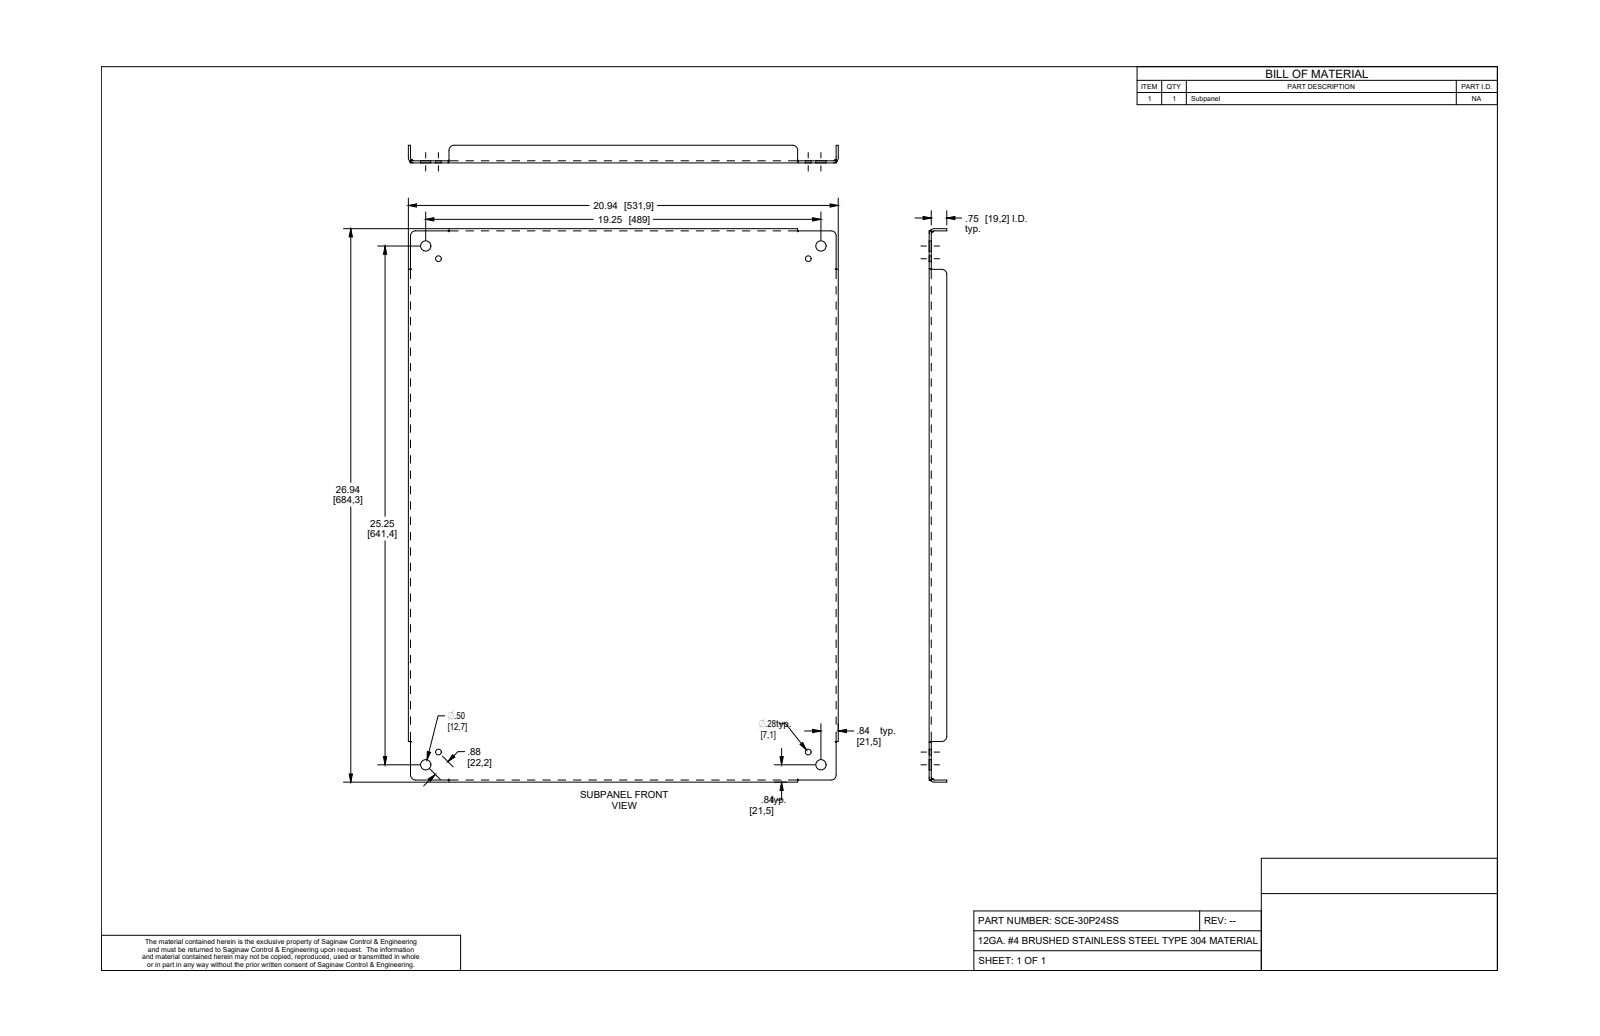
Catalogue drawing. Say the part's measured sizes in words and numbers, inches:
The part is named "SCE-30P24SS". Its 3-D file was written by "SolidWorks 2019 (CONFIG_CONTROL_DESIGN)". It is 1 solid with 82 faces: 30 planar, 28 cylindrical and 24 other. Overall it measures 26.941 by 20.941 by 0.858 inches. Its volume is 63.96 cubic inches and its surface area 1 241 square inches. Round holes: 4 of diameter 0.281, 4 of diameter 0.5. Partial cylindrical surfaces (rounded edges, fillets, slot ends): 8 of radius 0.25, 4 of radius 0.246, 2 of radius 0.142, 2 of radius 0.143. The main face-to-face distances are 0.104, 20.838, 26.838, 20.734, 20.942, 26.734, 26.942, 0.754, 0.858, 1.979. The hole center spacings are 0.875, 18.643, 24.641, 30.887, 18.014, 19.252, 24.014, 25.252.
